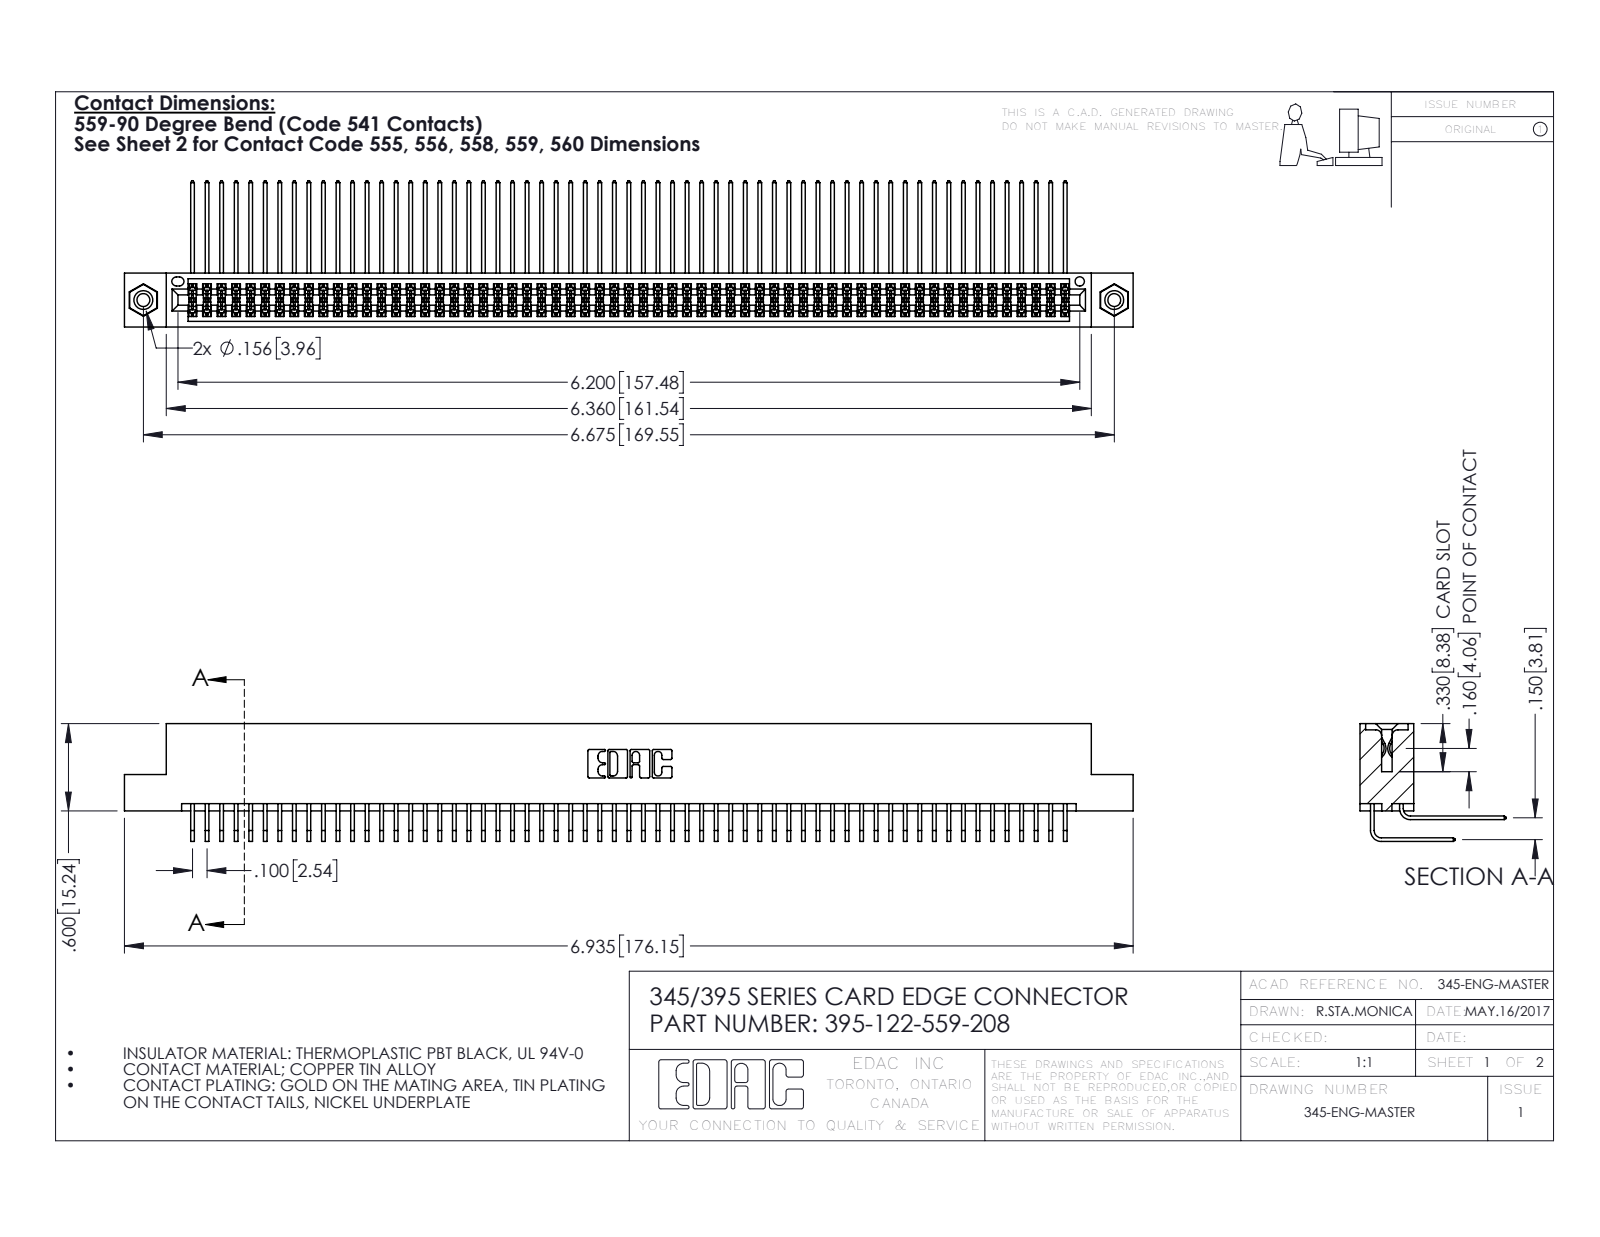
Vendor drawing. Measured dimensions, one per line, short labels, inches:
name: 345-292-001_559 Tail - 2; 395-122-559-208; 345 Part_Flush Mounting Lugs - 0.156 Dia-TI; 345-250-001_345-250-003-102 (+1 more)
written by: SolidWorks 2016 (CONFIG_CONTROL_DESIGN)
unit: in
bodies: 125 solids, 6530 faces (4382 planar, 2132 cylindrical, 16 other)
size: 6.935 × 1.005 × 0.809
volume: 1.098 in³; area: 46.93 in²
holes: 2× ⌀0.089, 2× ⌀0.125, 2× ⌀0.156, 1× ⌀0.064
bosses: 2× ⌀0.155
rounds: 183× R0.006, 22× R0.01, 6× R0.007, 6× R0.031, 3× R0.026, 2× R0.014, 2× R0.019, 2× R0.022
face distances: 0.072, 0.298, 0.2, 0.37, 0.098, 0.272, 0.025, 0.225, 0.175, 0.15
hole spacings: 0.27, 6.439, 6.675
